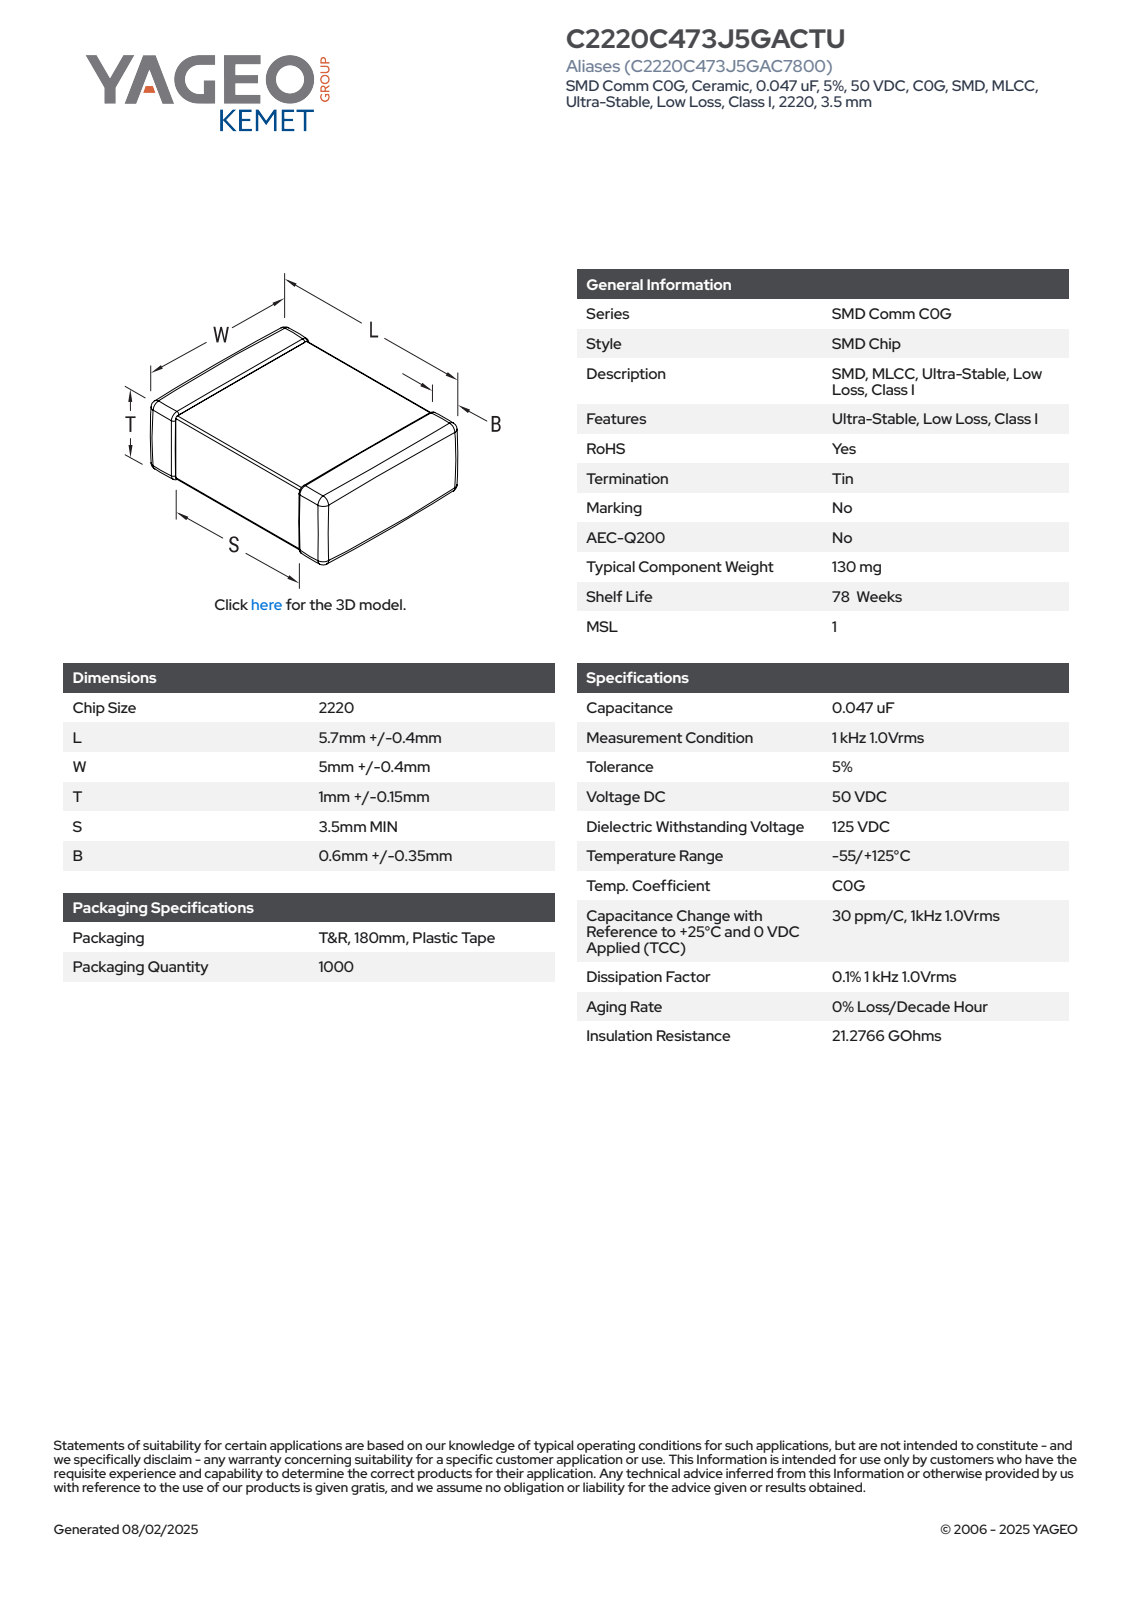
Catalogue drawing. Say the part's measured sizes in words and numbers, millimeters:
The part is named "CCS_CCSTDNOS_2220_L6.1W5.4T1.15B0.95". Its 3-D file was written by "SolidWorks 2014 (AUTOMOTIVE_DESIGN)". It is 4 solids with 125 faces: 71 planar, 38 cylindrical and 16 other. Overall it measures 6.1 by 5.4 by 1.15 millimeters. Its volume is 32 cubic millimeters and its surface area 89 square millimeters. Partial cylindrical surfaces (rounded edges, fillets, slot ends): 24 of radius 0.11. The main face-to-face distances are 0.93, 1.04, 1.15, 6.1, 5.18, 5.29, 5.4, 2.66, 2.74, 2.55.
